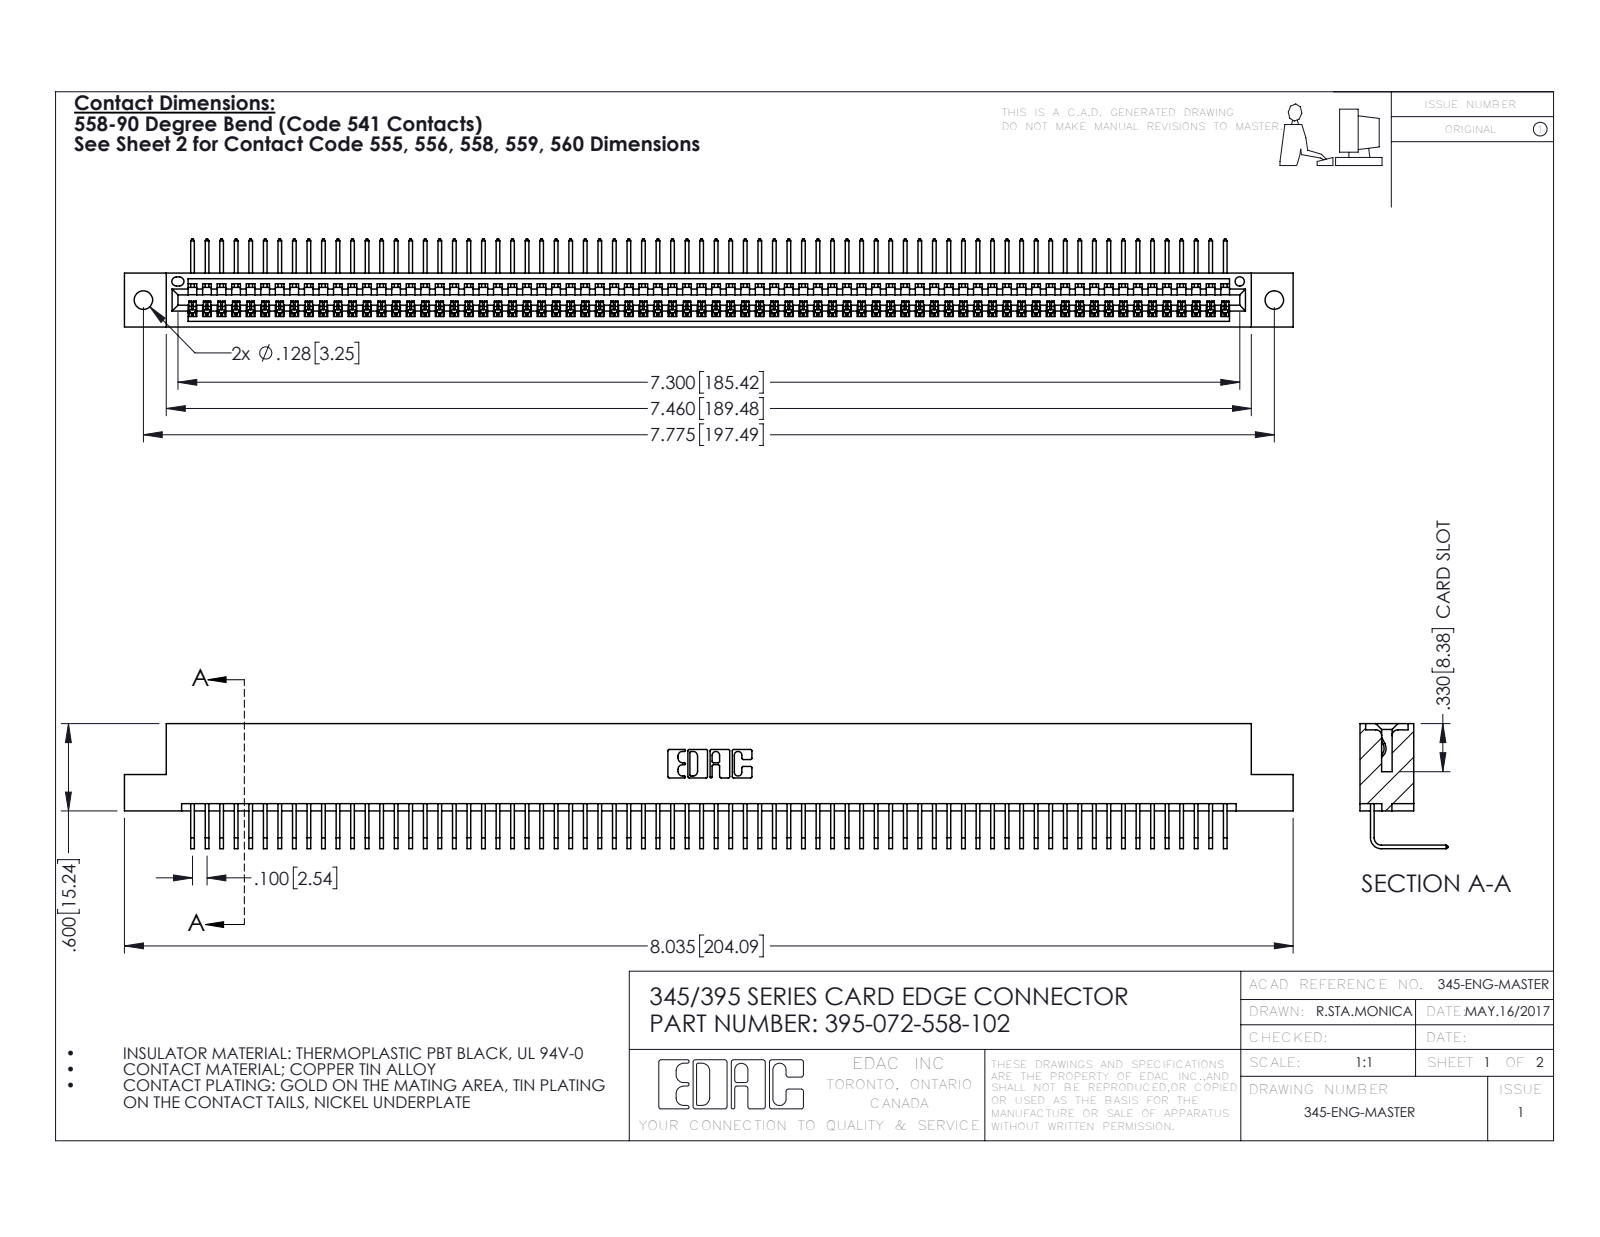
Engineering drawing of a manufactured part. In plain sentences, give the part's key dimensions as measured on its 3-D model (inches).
The part is named "395-072-558-102; 345-292-001_558 Tail - 2; 345 Part_Flush Mounting Lugs - 0.128 Dia". Its 3-D file was written by "SolidWorks 2016 (CONFIG_CONTROL_DESIGN)". It is 73 solids with 4446 faces: 3104 planar, 1342 cylindrical and 0 other. Overall it measures 8.035 by 0.859 by 0.605 inches. Its volume is 1.21 cubic inches and its surface area 43.25 square inches. Round holes: 2 of diameter 0.128, 1 of diameter 0.064. Partial cylindrical surfaces (rounded edges, fillets, slot ends): 144 of radius 0.006, 22 of radius 0.01, 6 of radius 0.007, 6 of radius 0.031, 3 of radius 0.026, 2 of radius 0.031, 2 of radius 0.04, 1 of radius 0.014. The main face-to-face distances are 0.298, 0.072, 0.37, 0.2, 0.098, 0.272, 0.025, 0.225, 0.149, 0.072. The hole center spacings are 0.27, 7.539, 7.775.
